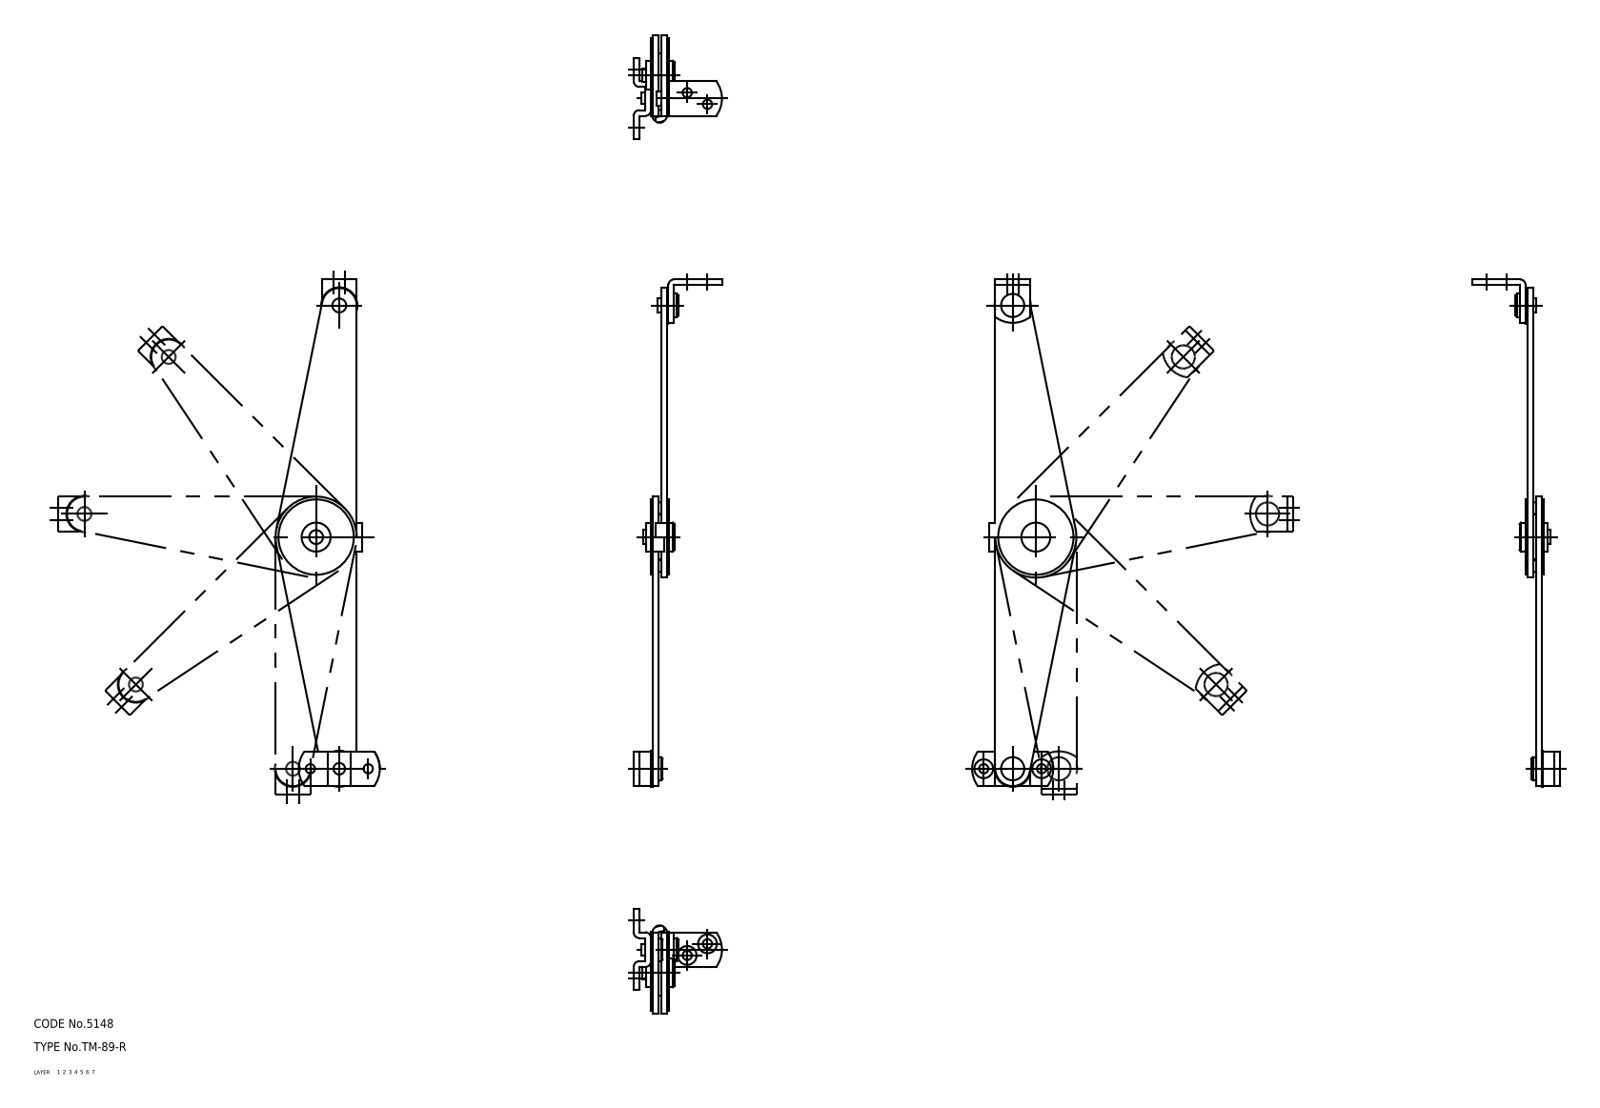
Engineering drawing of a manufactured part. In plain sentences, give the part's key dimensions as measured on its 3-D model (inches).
The part is named "ball_mr-1; ball_mr; spring_mr-1; arm_mr-1 (+8 more)". Its 3-D file was written by "CADfix (AUTOMOTIVE_DESIGN)". It is 15 solids with 155 faces: 0 planar, 0 cylindrical and 155 other. Overall it measures 6.9 by 1.417 by 1.201 inches. Its volume is 0.665 cubic inches and its surface area 23.2 square inches.
